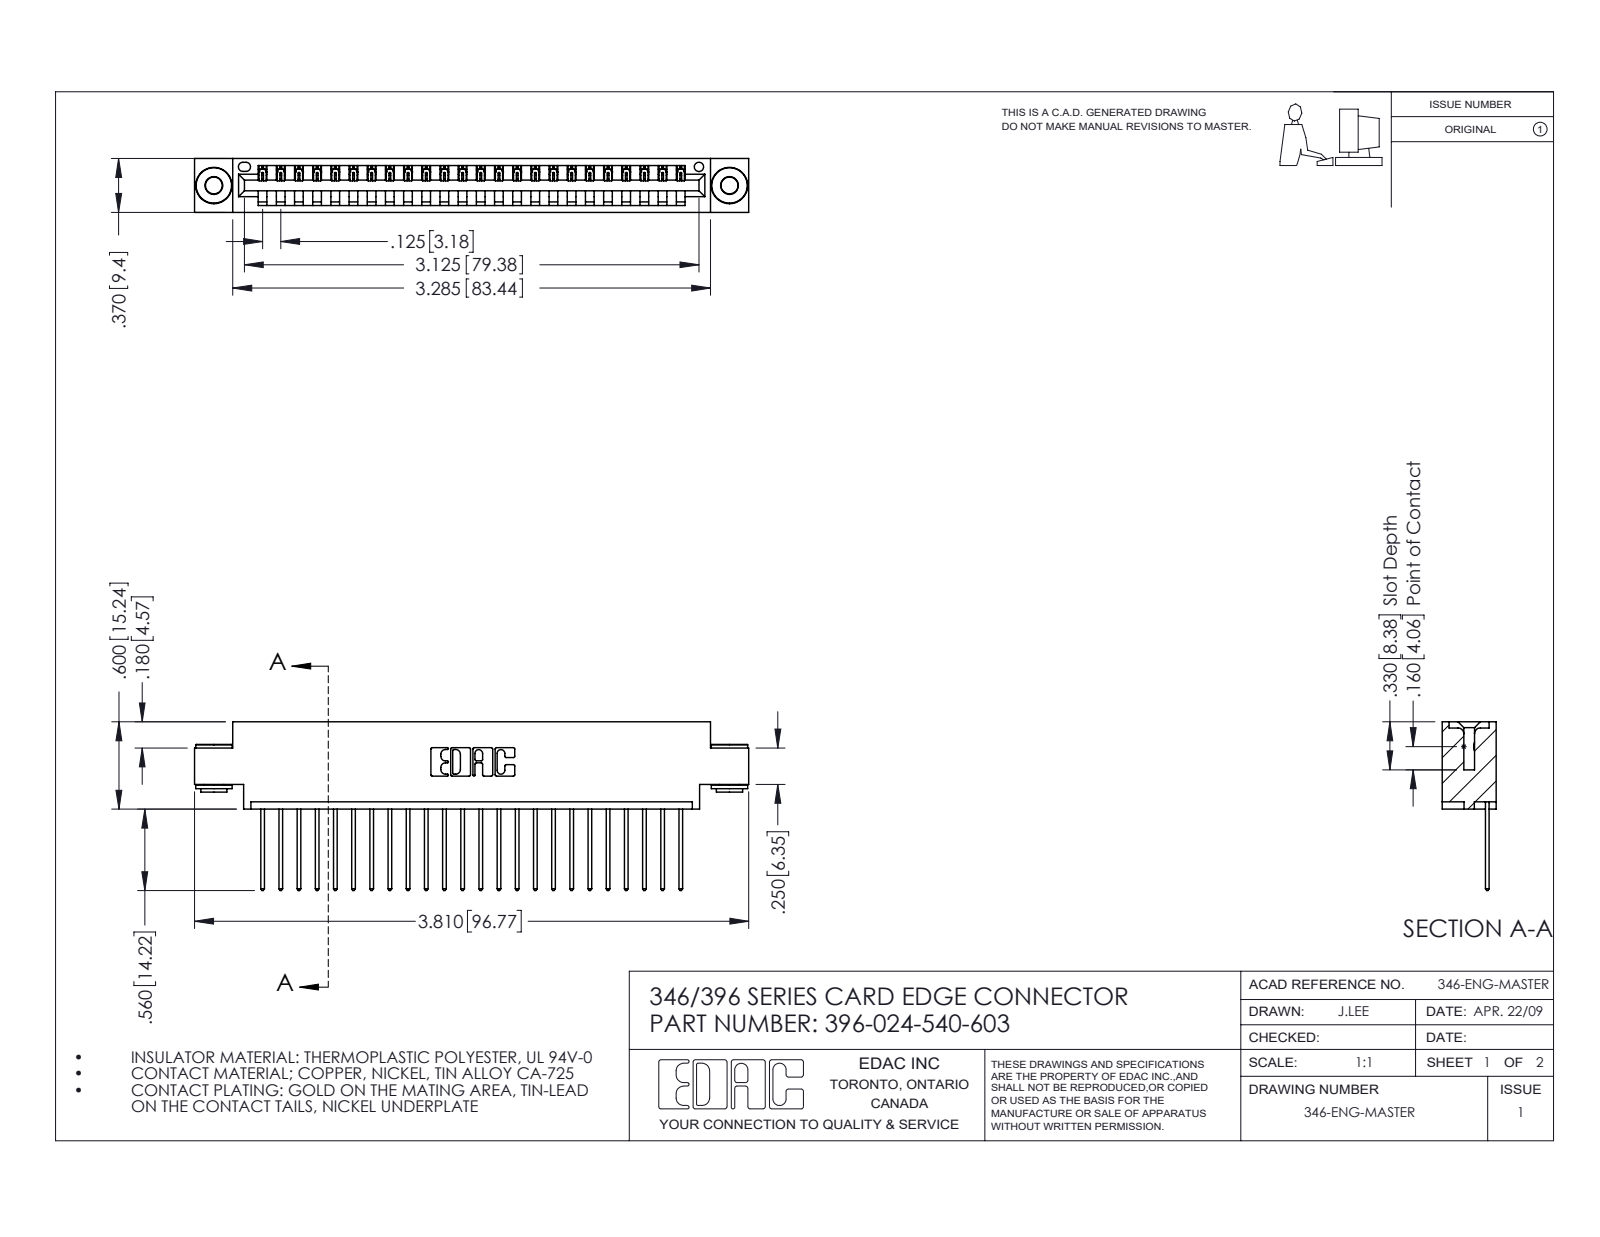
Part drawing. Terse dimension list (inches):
name: 345-250-002_345-250-002-102; 396-024-540-603; 346 Part_0.170 Offset - 0.156 Dia-TH; 345-292-001_345-293-140
written by: SolidWorks 2016 (CONFIG_CONTROL_DESIGN)
unit: in
bodies: 27 solids, 1556 faces (1050 planar, 498 cylindrical, 8 other)
size: 3.81 × 1.16 × 0.37
volume: 0.551 in³; area: 18.16 in²
holes: 2× ⌀0.116, 2× ⌀0.156, 1× ⌀0.064
bosses: 2× ⌀0.25, 2× ⌀0.18, 2× ⌀0.136
rounds: 48× R0.006, 48× R0.01, 22× R0.01, 6× R0.007, 6× R0.031, 3× R0.026, 2× R0.031, 2× R0.04
face distances: 0.048, 0.322, 0.37, 0.25, 0.025, 0.072, 0.298, 0.148, 0.222, 0.1
hole spacings: 0.246, 3.337, 3.545
